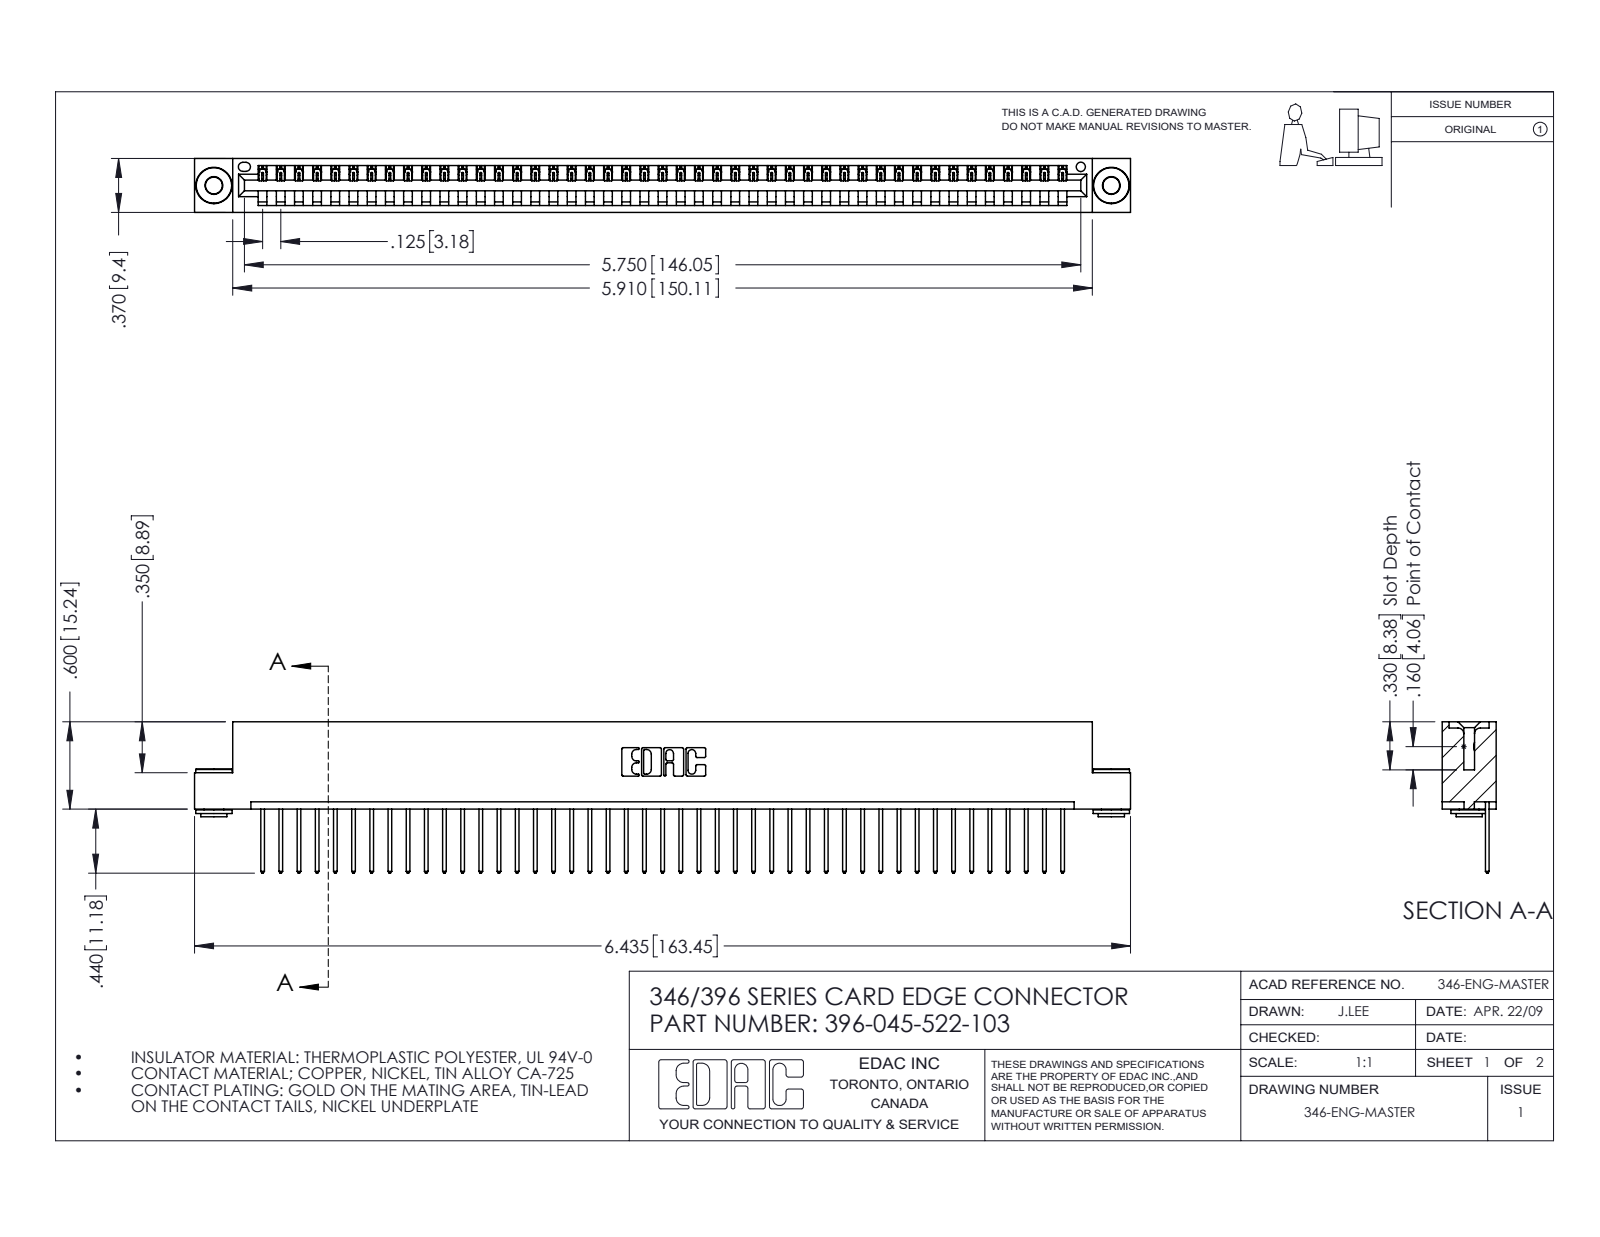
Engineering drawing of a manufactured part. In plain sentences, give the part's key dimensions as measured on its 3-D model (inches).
The part is named "396-045-522-103; 345-250-002_345-250-002-102; 346 Part_Flush Mounting Lugs - 0.156 Dia-TH; 345-292-001_345-293-122". Its 3-D file was written by "SolidWorks 2016 (CONFIG_CONTROL_DESIGN)". It is 48 solids with 2770 faces: 1886 planar, 876 cylindrical and 8 other. Overall it measures 6.435 by 1.04 by 0.37 inches. Its volume is 0.958 cubic inches and its surface area 31.05 square inches. Round holes: 2 of diameter 0.116, 2 of diameter 0.156, 1 of diameter 0.064. Round bosses or shafts: 2 of diameter 0.25, 2 of diameter 0.18, 2 of diameter 0.136. Partial cylindrical surfaces (rounded edges, fillets, slot ends): 90 of radius 0.006, 90 of radius 0.01, 22 of radius 0.01, 6 of radius 0.007, 6 of radius 0.031, 3 of radius 0.026, 2 of radius 0.031, 2 of radius 0.04. The main face-to-face distances are 0.048, 0.322, 0.37, 0.25, 0.025, 0.072, 0.298, 0.148, 0.222, 0.1. The hole center spacings are 0.246, 5.961, 6.17.
